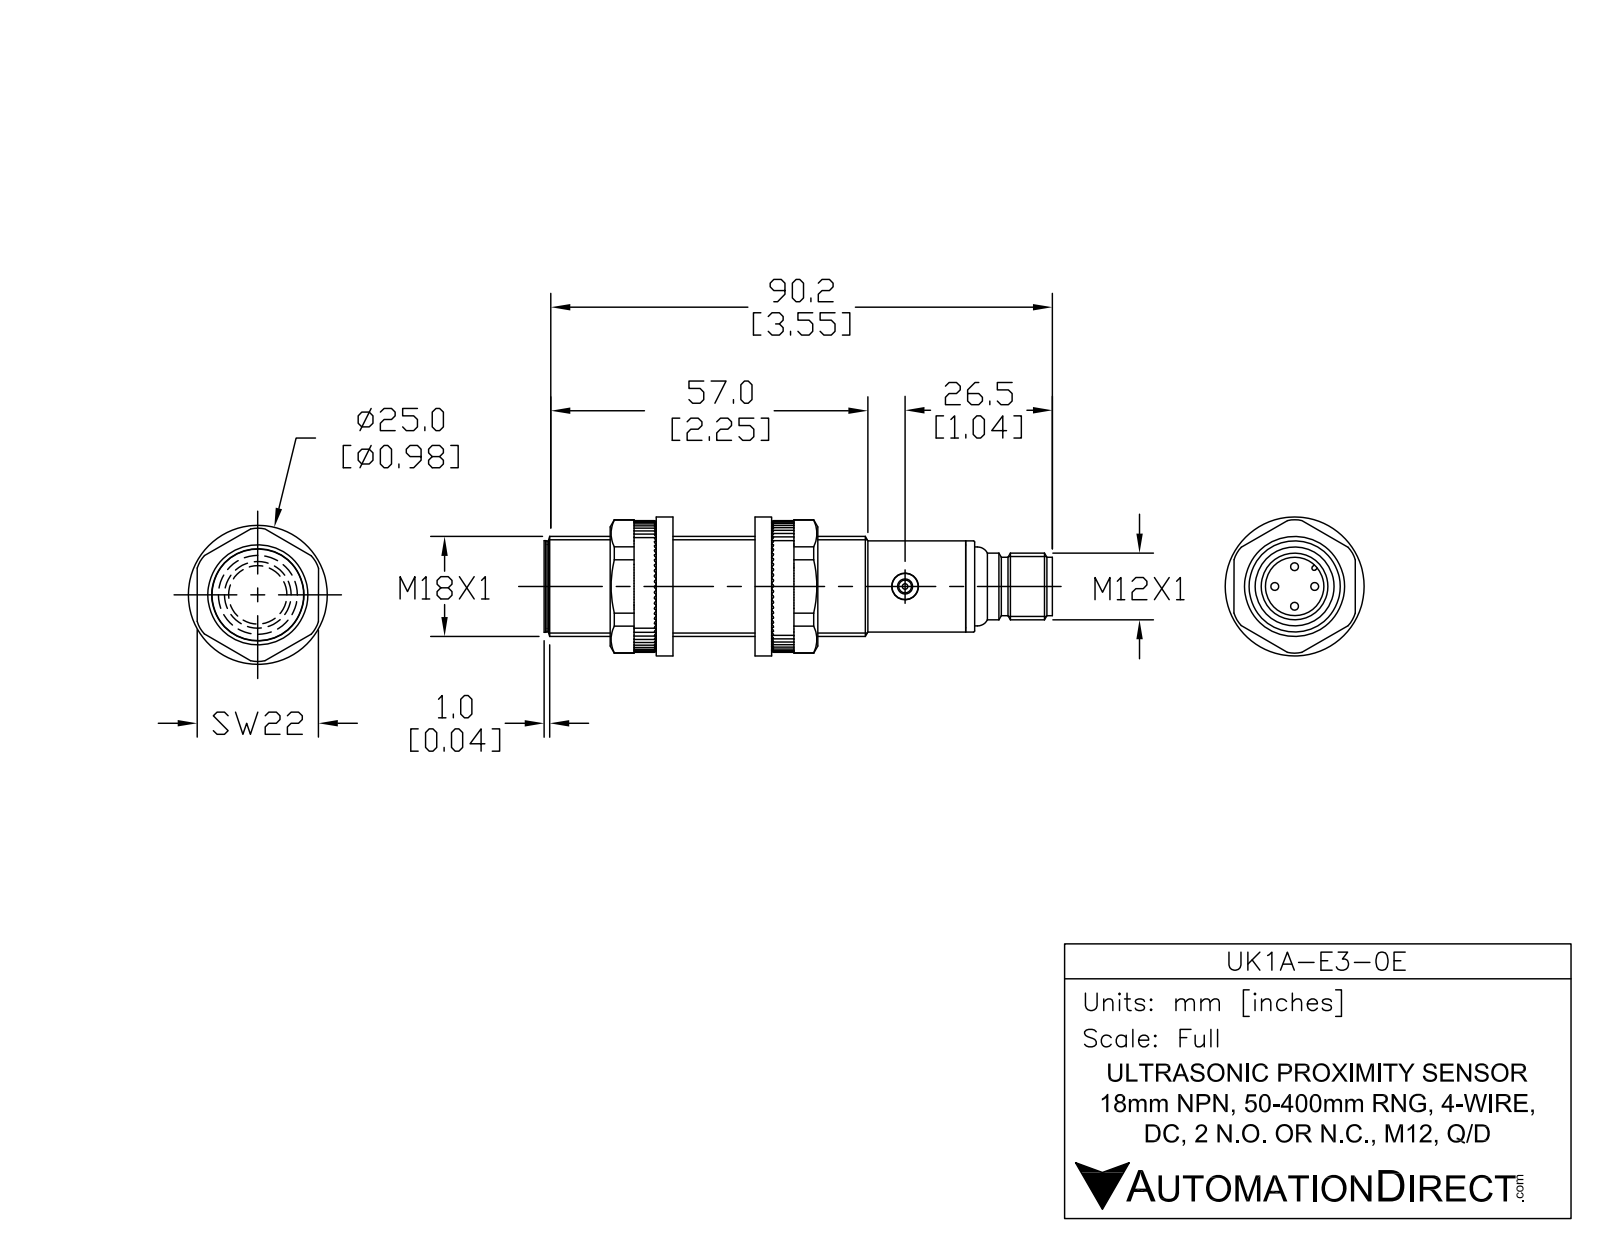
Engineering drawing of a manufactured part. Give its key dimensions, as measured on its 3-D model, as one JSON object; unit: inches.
{"part_name": "UK1A-E3-0E", "step_written_by": "SolidWorks 2017 (AUTOMOTIVE_DESIGN)", "units": "inches", "bodies": {"solids": 6, "faces": 106, "planar": 21, "cylindrical": 48, "other": 37}, "overall_size": [3.606, 0.709, 0.709], "volume_in3": 1.202, "surface_area_in2": 10.68, "round_holes": [[0.106, 1], [0.185, 1], [0.276, 1], [0.327, 1], [0.374, 1]], "round_bosses_or_shafts": [[0.039, 4], [0.709, 1], [0.654, 1], [0.646, 1], [0.622, 1], [0.559, 1], [0.472, 1], [0.413, 1]], "partial_cylinders_radius": [[0.024, 1]], "face_to_face_distances": [2.957, 0.039, 2.996, 0.037, 2.994, 0.043, 0.157, 3.055, 3.053, 3.016]}
